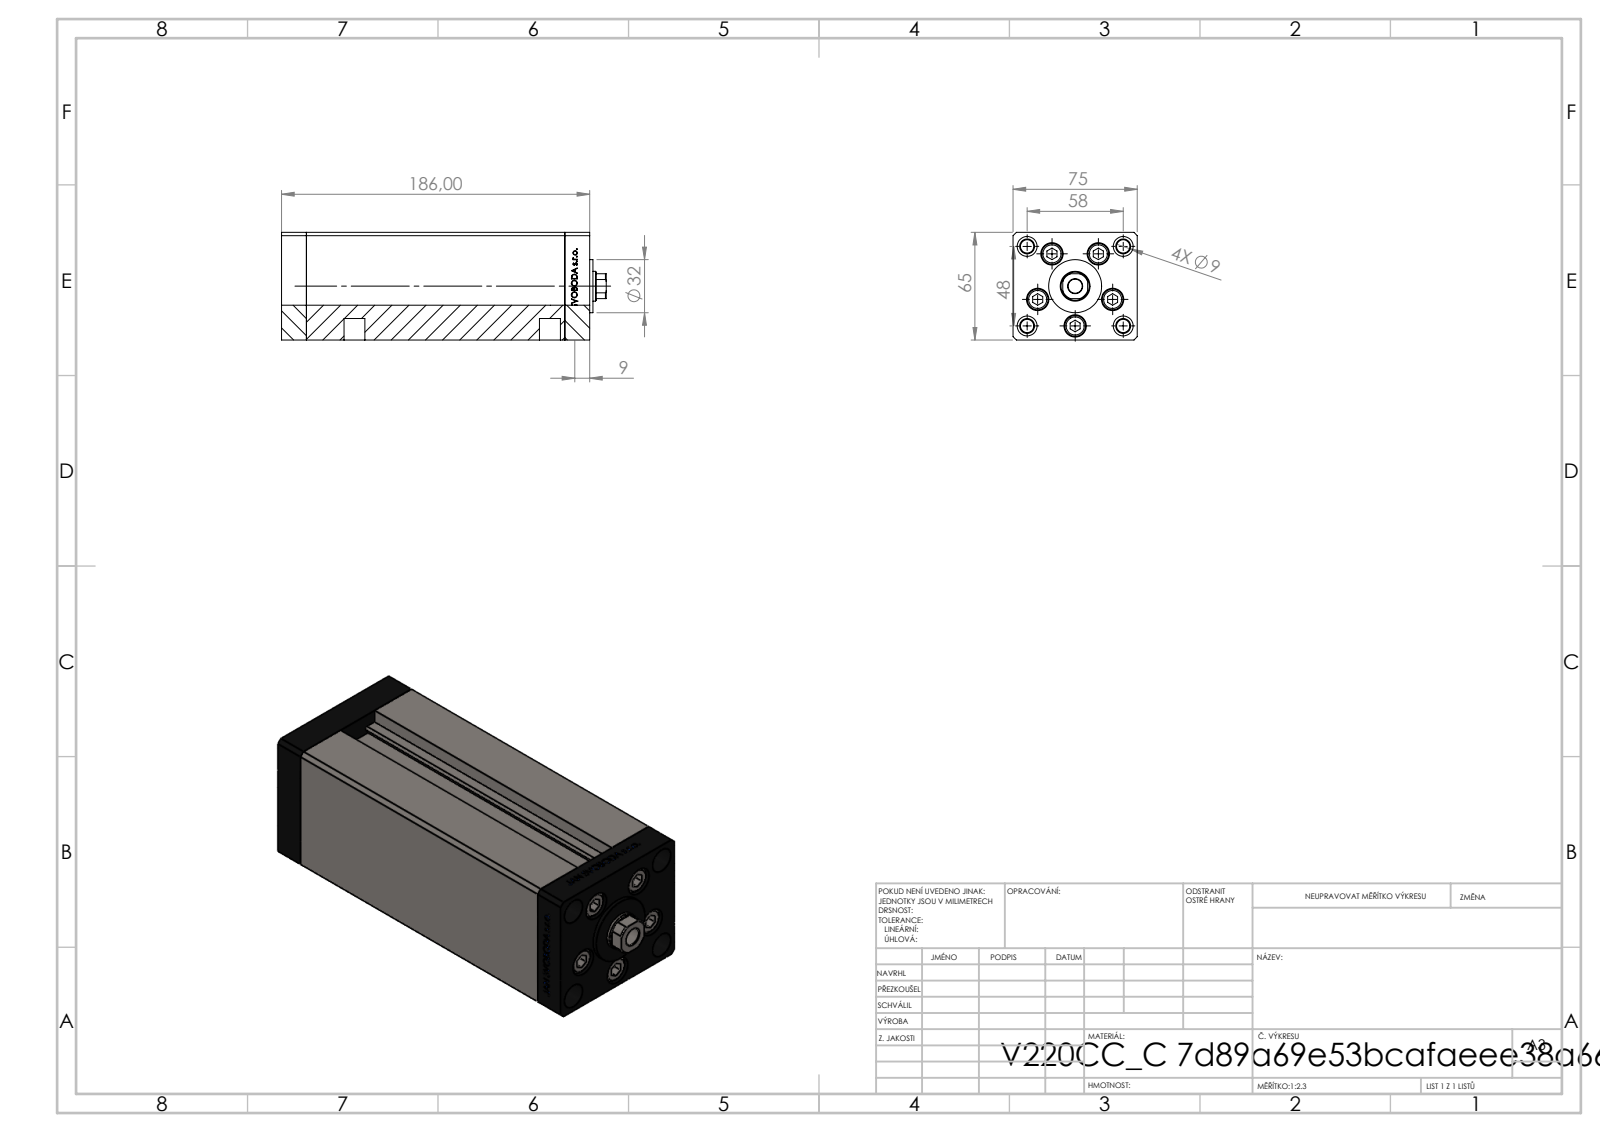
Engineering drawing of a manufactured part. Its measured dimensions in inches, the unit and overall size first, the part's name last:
Units: inches
Overall size (bounding box): 7.717 × 2.953 × 2.559
Round holes (diameter × count): ⌀0.354 ×9, ⌀0.531 ×5, ⌀0.079 ×4, ⌀0.315 ×4, ⌀0.472 ×4, ⌀0.518 ×4, ⌀0.335 ×1, ⌀0.492 ×1, ⌀0.709 ×1
Round bosses / shafts (diameter × count): ⌀0.315 ×5, ⌀0.492 ×4, ⌀1.26 ×1
Partial cylindrical surfaces — rounded edges, fillets, slot ends (radius × count): R0.037 ×2, R0.335 ×1
Main face-to-face distances: 2.953, 2.559, 0.591, 6.142, 6.732, 7.323, 1.102, 0.512, 2.146, 0.413
Hole centre spacings: 0.945, 1.482, 0.617, 0.678, 1.091, 1.135, 1.142, 1.285
Volume: 46.03 in³ · Surface area: 240.4 in²
Bodies: 13 solids, 1179 faces (542 planar, 175 cylindrical, 462 other)
Part name (STEP PRODUCT): V220C_VC_C; V220C FRONT; V220C_C MIDDLE; ALLEN BOLT (+1 more)
STEP written by: SolidWorks 2019 (CONFIG_CONTROL_DESIGN)
